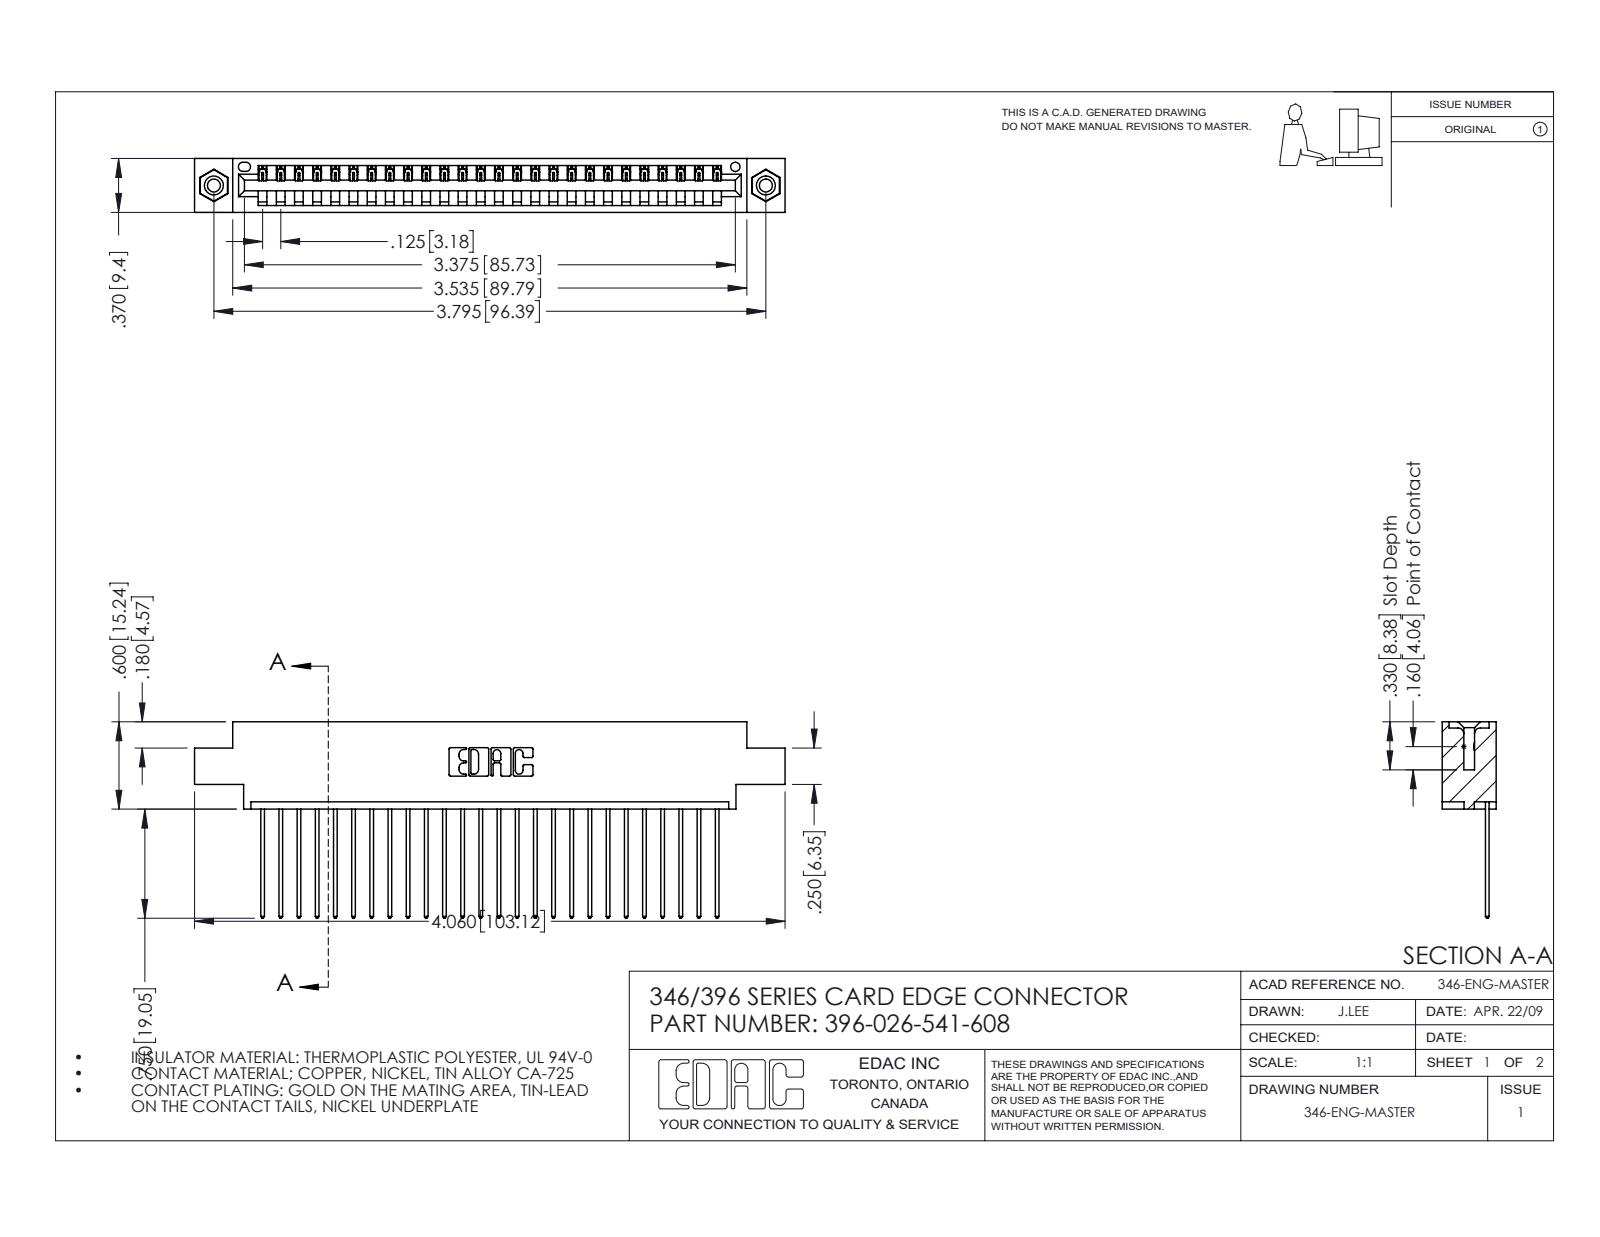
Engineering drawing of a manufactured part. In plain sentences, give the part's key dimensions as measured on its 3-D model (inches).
The part is named "346 Part_0.170 Offset - 0.156 Dia-TI; 345-250-001_345-250-003-102; 396-026-541-608; 345-292-001_345-293-141". Its 3-D file was written by "SolidWorks 2016 (CONFIG_CONTROL_DESIGN)". It is 29 solids with 1694 faces: 1152 planar, 526 cylindrical and 16 other. Overall it measures 4.06 by 1.35 by 0.37 inches. Its volume is 0.591 cubic inches and its surface area 19.57 square inches. Round holes: 2 of diameter 0.089, 2 of diameter 0.125, 2 of diameter 0.156, 1 of diameter 0.064. Round bosses or shafts: 2 of diameter 0.155. Partial cylindrical surfaces (rounded edges, fillets, slot ends): 52 of radius 0.006, 52 of radius 0.01, 22 of radius 0.01, 6 of radius 0.007, 6 of radius 0.031, 3 of radius 0.026, 2 of radius 0.031, 2 of radius 0.04. The main face-to-face distances are 0.048, 0.322, 0.37, 0.25, 0.072, 0.298, 0.025, 0.222, 0.148, 0.1. The hole center spacings are 0.246, 3.587, 3.795.
